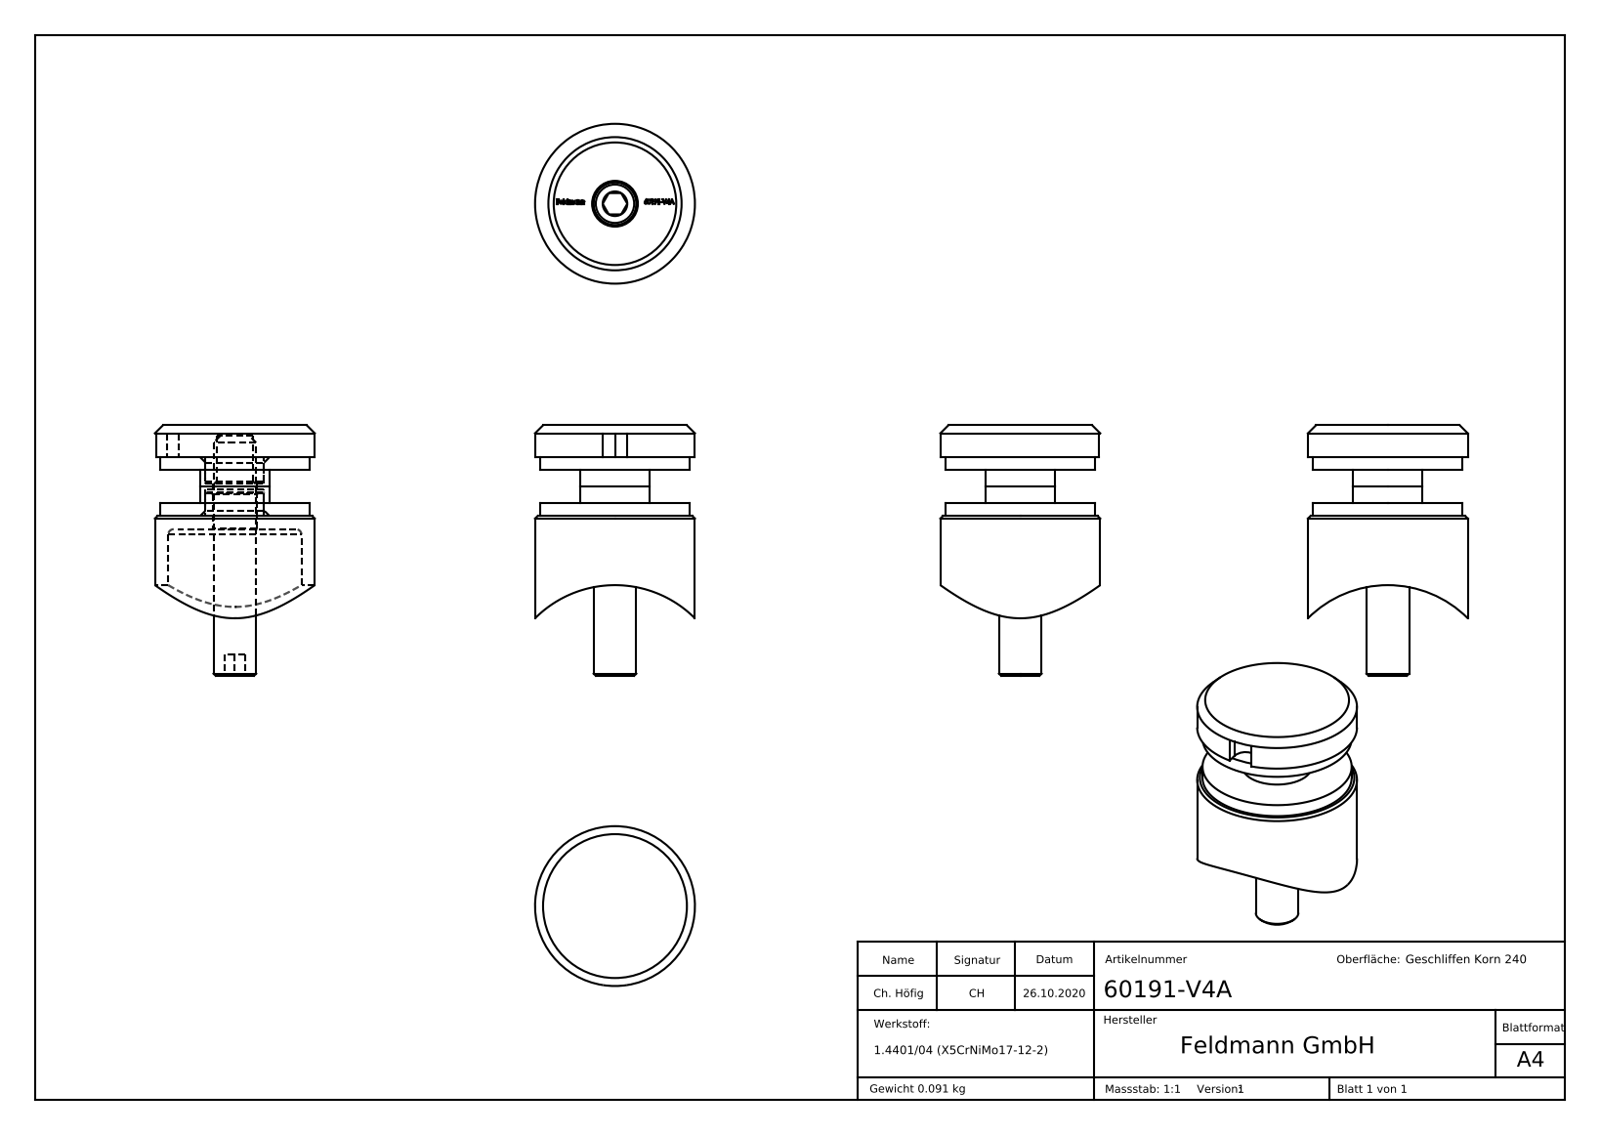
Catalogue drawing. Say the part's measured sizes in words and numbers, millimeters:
The part is named "DIN913 M8x45_DIN913 M8x45; DIN913 M8x45; 60190-240 Teil2; 60191-V4A (+5 more)". Its 3-D file was written by "SolidWorks 2018 (CONFIG_CONTROL_DESIGN)". It is 5 solids with 295 faces: 159 planar, 35 cylindrical and 101 other. Overall it measures 47 by 30 by 30 millimeters. Its volume is 13 753 cubic millimeters and its surface area 10 884 square millimeters. Round holes: 1 of diameter 6.8, 1 of diameter 8.2, 1 of diameter 11, 1 of diameter 25. Round bosses or shafts: 1 of diameter 30, 1 of diameter 28, 1 of diameter 13, 1 of diameter 8. Partial cylindrical surfaces (rounded edges, fillets, slot ends): 1 of radius 2.25, 1 of radius 21.2. The main face-to-face distances are 11, 2.4, 8.6, 6, 17, 8.4, 6.2, 14.6, 2.5, 4.9.
